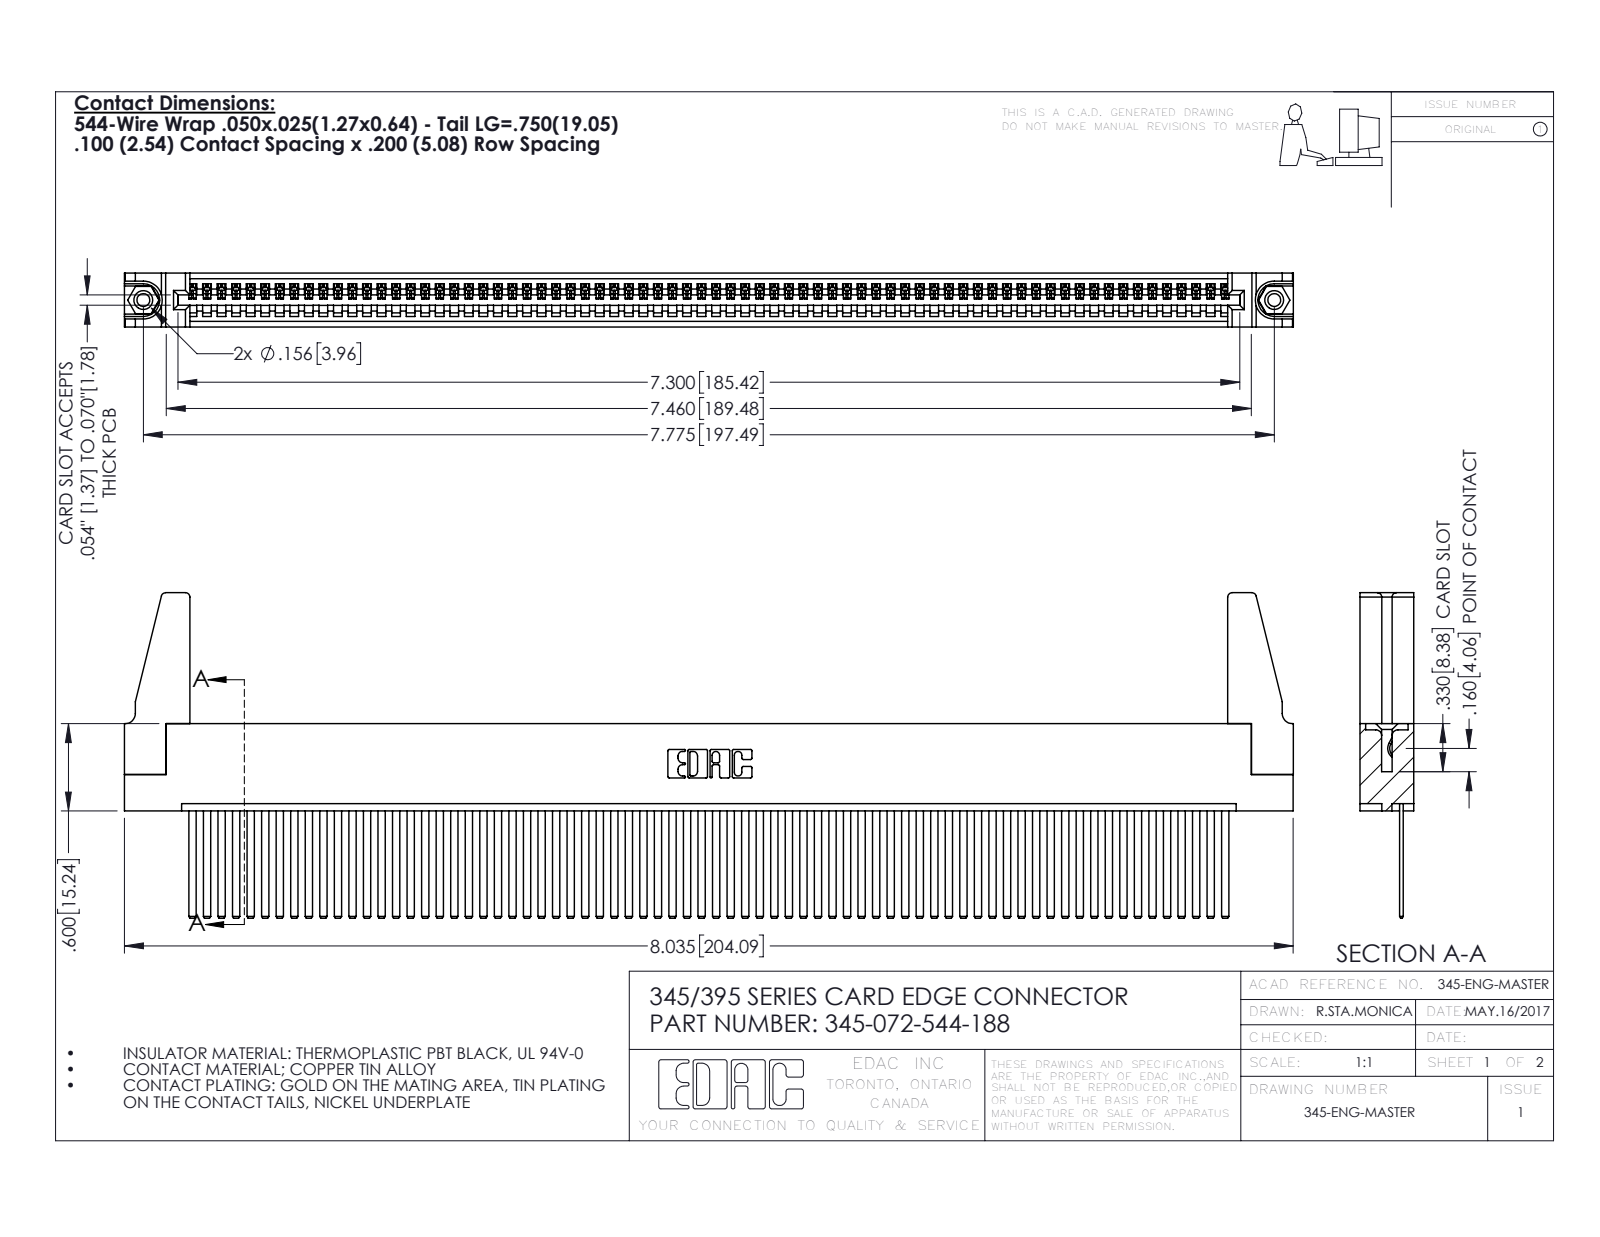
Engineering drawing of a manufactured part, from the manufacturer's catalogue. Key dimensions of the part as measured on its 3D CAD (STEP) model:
Part name (STEP PRODUCT): 345-220-078_345-220-088; 345-292-001_345-293-144; 345-072-544-188; 345 Part_Flush Mounting Lugs - 0.156 Dia-TH (+1 more)
STEP written by: SolidWorks 2016 (CONFIG_CONTROL_DESIGN)
Units: inches
Bodies: 77 solids, 3994 faces (2744 planar, 1234 cylindrical, 16 other)
Overall size (bounding box): 8.036 × 2.237 × 0.37
Volume: 1.447 in³ · Surface area: 51.52 in²
Round holes (diameter × count): ⌀0.089 ×2, ⌀0.125 ×2, ⌀0.156 ×2, ⌀0.064 ×1
Round bosses / shafts (diameter × count): ⌀0.155 ×2
Partial cylindrical surfaces — rounded edges, fillets, slot ends (radius × count): R0.006 ×144, R0.01 ×22, R0.03 ×8, R0.007 ×6, R0.031 ×6, R0.026 ×3, R0.031 ×2, R0.04 ×2
Main face-to-face distances: 0.072, 0.298, 0.098, 0.272, 0.025, 0.37, 0.2, 0.225, 0.149, 0.072
Hole centre spacings: 0.27, 7.539, 7.775
